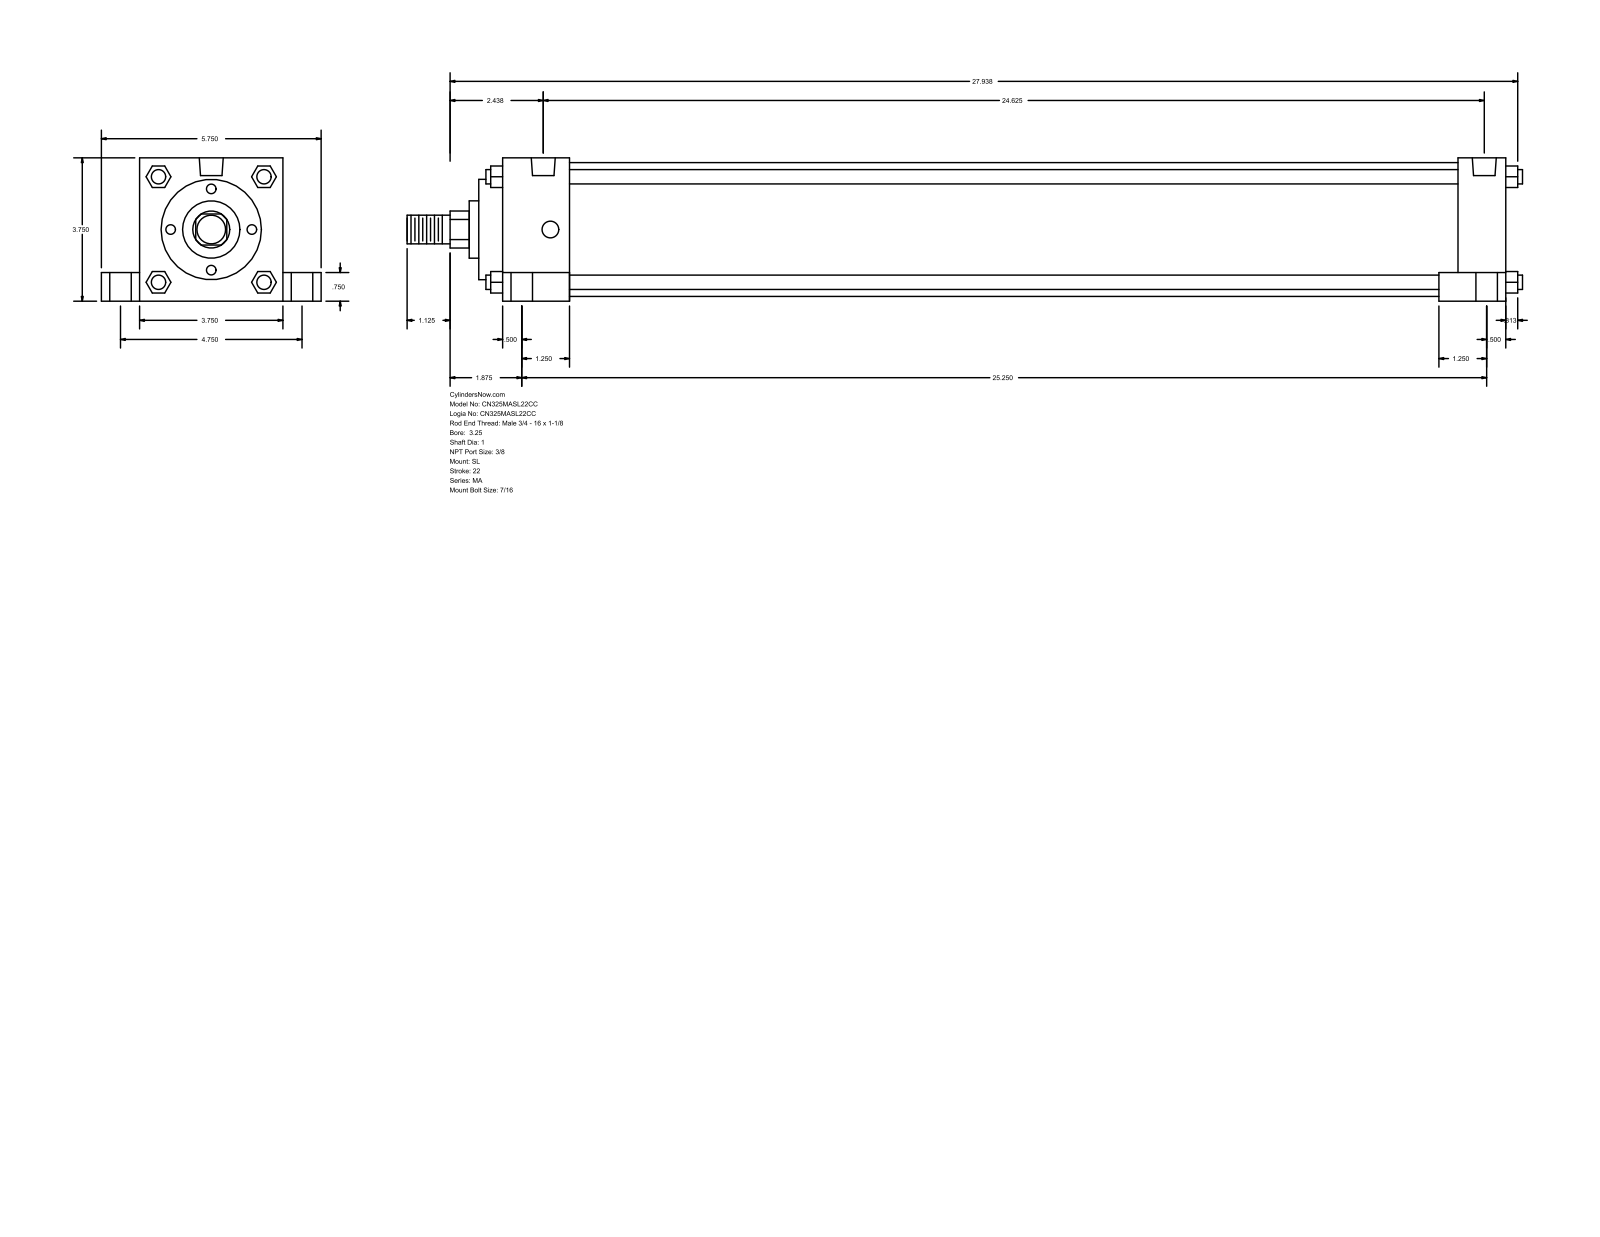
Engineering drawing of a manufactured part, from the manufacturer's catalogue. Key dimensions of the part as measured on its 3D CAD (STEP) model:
Part name (STEP PRODUCT): MA_SL__0325_1
STEP written by: GSSL Pune (CONFIG_CONTROL_DESIGN)
Units: millimetres
Bodies: 0 solids, 150 faces (113 planar, 37 cylindrical, 0 other)
Overall size (bounding box): 741.36 × 146.05 × 95.25
Round holes (diameter × count): ⌀11.11 ×4, ⌀14.29 ×4, ⌀20.64 ×4, ⌀15.93 ×2
Round bosses / shafts (diameter × count): ⌀9.53 ×4, ⌀88.9 ×1, ⌀66.67 ×1, ⌀38.1 ×1, ⌀25.4 ×1, ⌀19.05 ×1
Partial cylindrical surfaces — rounded edges, fillets, slot ends (radius × count): R12.29 ×1
Main face-to-face distances: 95.24, 666.75, 15.87, 25.41, 120.65, 682.62, 19.05, 635, 31.75, 44.46
Hole centre spacings: 60.35, 60.66, 62, 63.27, 120.66, 615.95, 625.23, 629.97
